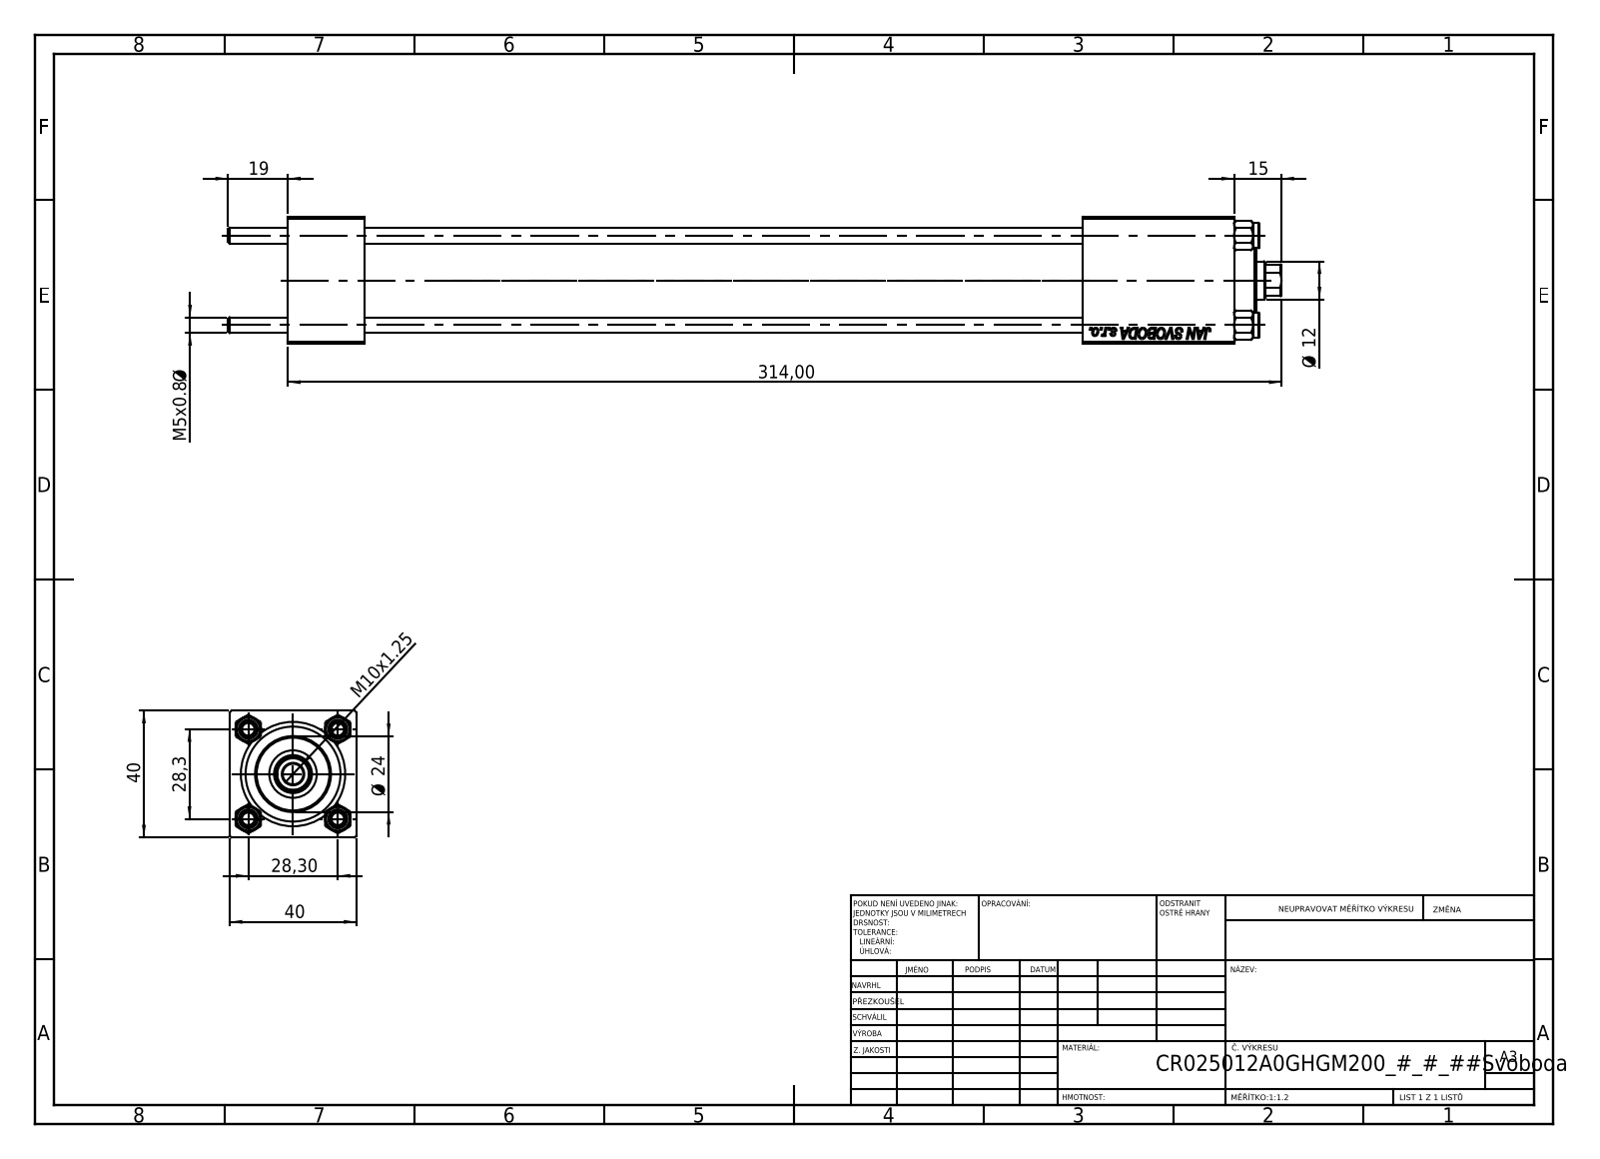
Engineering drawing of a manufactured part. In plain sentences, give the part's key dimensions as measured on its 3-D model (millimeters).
The part is named "V215_VC_A; V215CR_VCP; NUT_M5; V215CR_BODY_A (+1 more)". Its 3-D file was written by "SolidWorks 2019 (CONFIG_CONTROL_DESIGN)". It is 11 solids with 1131 faces: 517 planar, 78 cylindrical and 536 other. Overall it measures 333 by 40 by 40 millimeters. Its volume is 226 820 cubic millimeters and its surface area 108 634 square millimeters. Round holes: 4 of diameter 5, 3 of diameter 20, 2 of diameter 7, 2 of diameter 13.16, 1 of diameter 6.5, 1 of diameter 12, 1 of diameter 15, 1 of diameter 25, 1 of diameter 30. Round bosses or shafts: 4 of diameter 8, 1 of diameter 31, 1 of diameter 24. Partial cylindrical surfaces (rounded edges, fillets, slot ends): 1 of radius 5.5. The main face-to-face distances are 40, 24, 299, 275, 270.3, 246.3, 28.7, 251, 227, 19.3. The hole center spacings are 20.01, 28.3, 40.02, 252.
